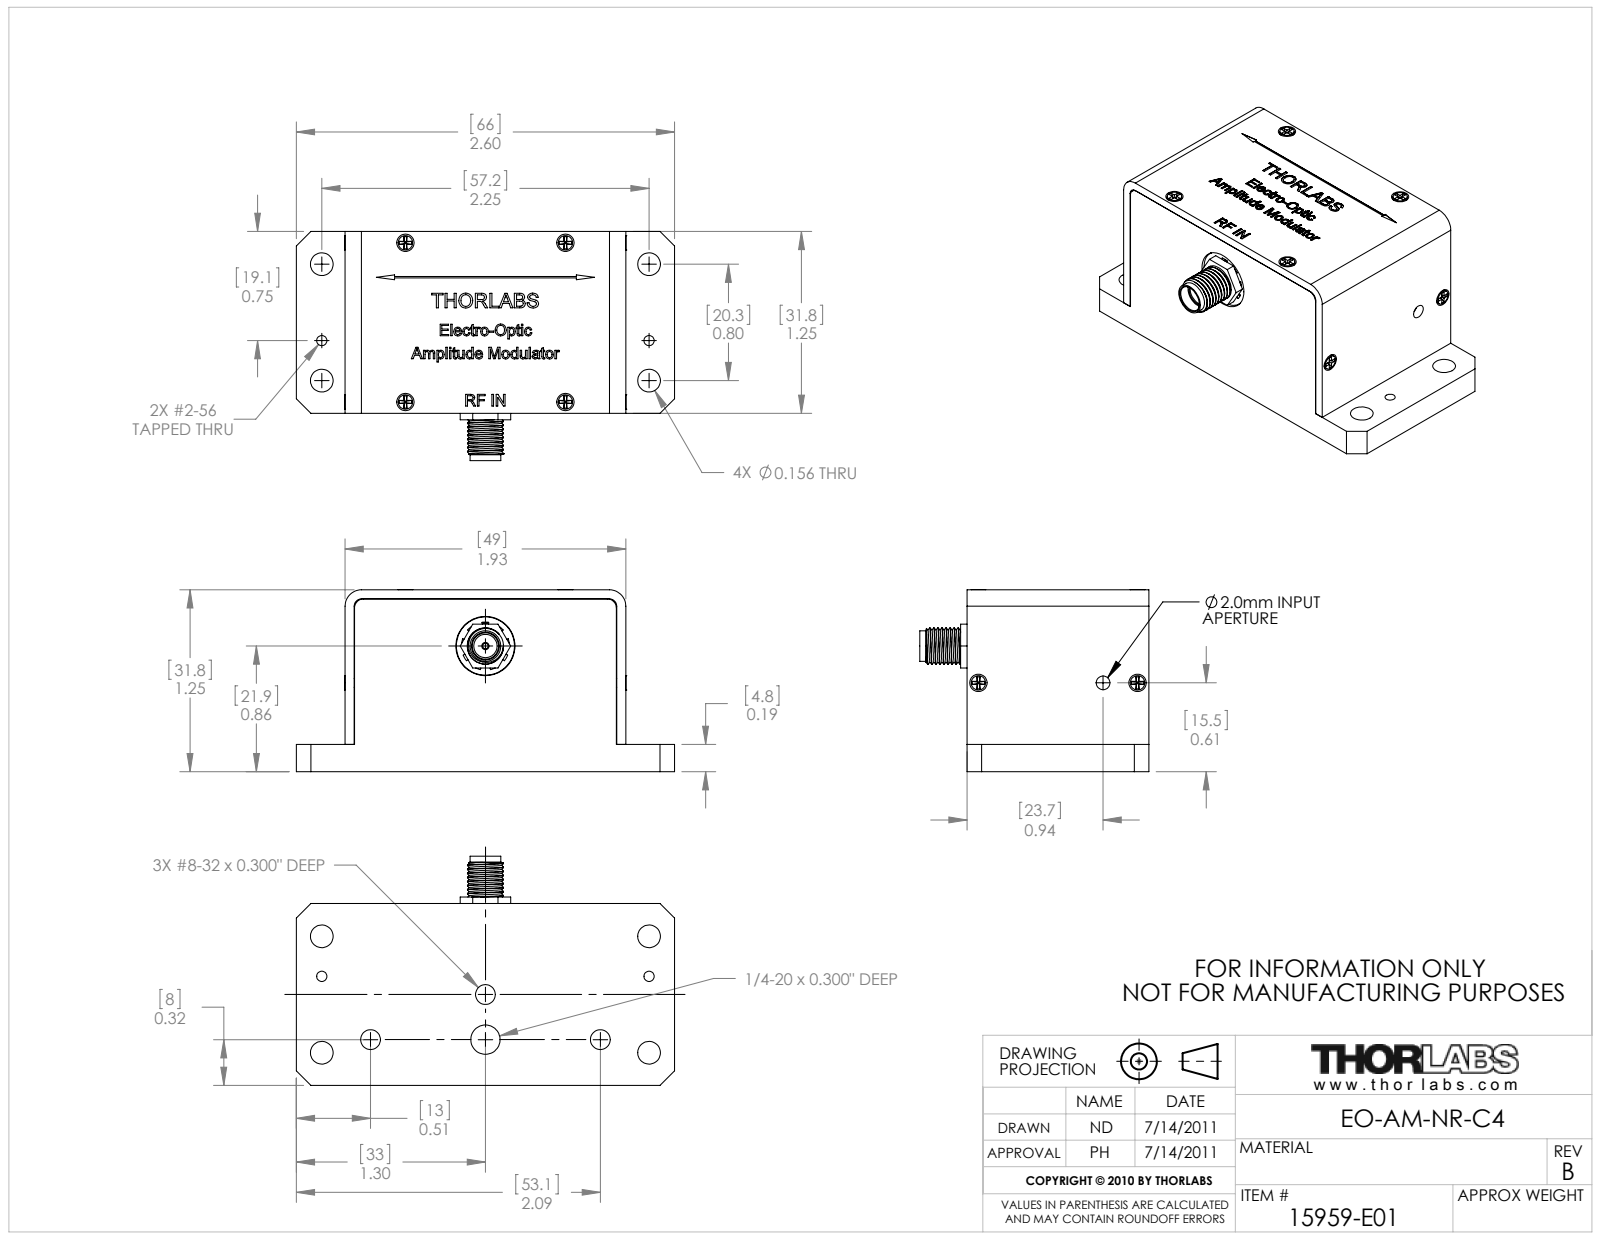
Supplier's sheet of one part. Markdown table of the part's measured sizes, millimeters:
| quantity | value |
| --- | --- |
| part name | 15959-E01 |
| STEP written by | SolidWorks 2011 (AUTOMOTIVE_DESIGN) |
| units | millimeters |
| bodies | 13 solids, 1048 faces (588 planar, 172 cylindrical, 288 other) |
| overall size | 66.04 × 40.01 × 31.79 |
| volume | 28 212 mm³ |
| surface area | 18 817 mm² |
| round holes (diameter × count) | 1.78 × 8, 1.19 × 6, 3.96 × 4, 3.45 × 3, 0.94 × 1, 1.27 × 1, 2.38 × 1, 4.06 × 1, 4.19 × 1, 4.6 × 1, 5.11 × 1, 6.35 × 1 |
| round bosses / shafts (diameter × count) | 2.51 × 6, 1.52 × 6, 10.16 × 1, 8 × 1, 6.3 × 1, 5.33 × 1, 1.27 × 1 |
| partial cylindrical surfaces (radius × count) | 1.59 × 5, 1.27 × 2, 2.86 × 2, 3.26 × 2, 3.49 × 1, 4.19 × 1 |
| main face-to-face distances | 31.76, 3.18, 28.58, 30.18, 1.59, 47.43, 25.4, 1.58, 8.89, 21.29 |
| hole center spacings | 15.08, 19.7, 28.14, 30.33, 42.71, 48.88, 27.78, 57.16 |
